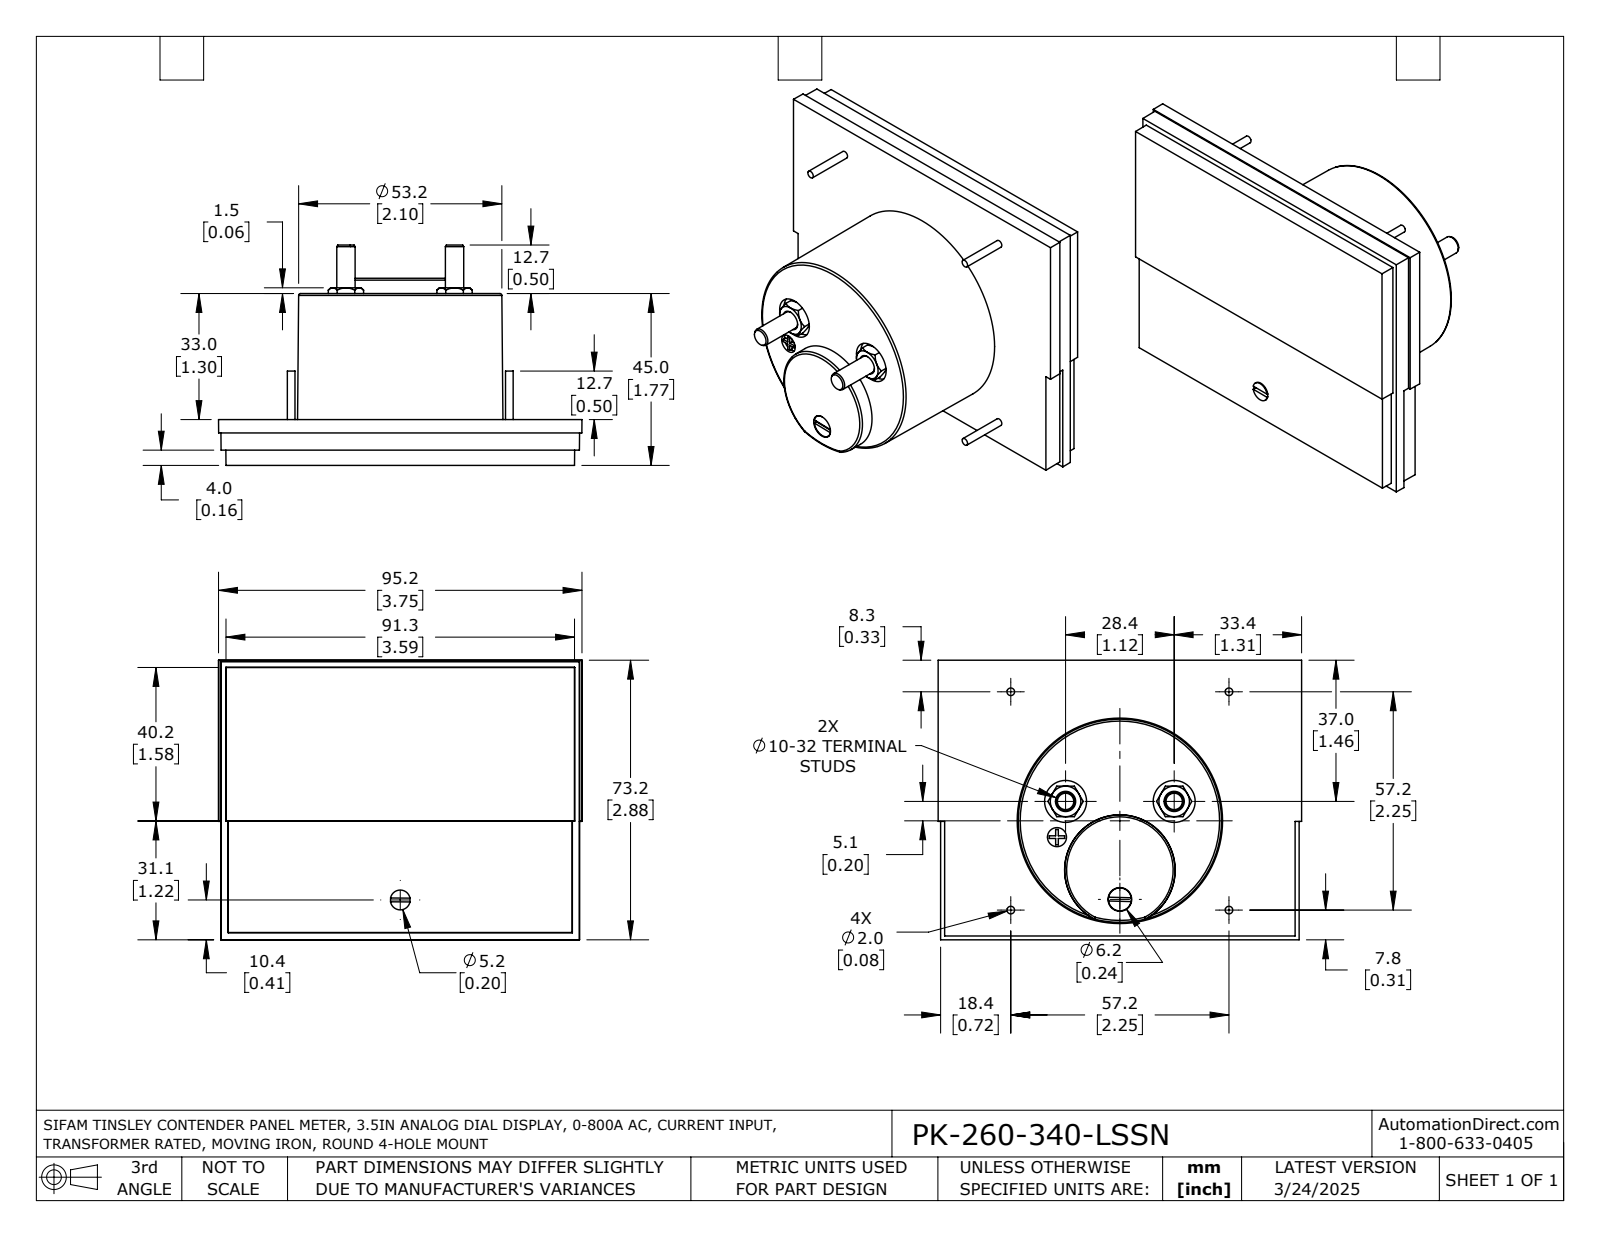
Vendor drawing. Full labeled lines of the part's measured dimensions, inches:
Part name (STEP PRODUCT): PK-260-340-LSSN
STEP written by: SolidWorks 2021 (AUTOMOTIVE_DESIGN)
Units: inches
Bodies: 1 solid, 163 faces (76 planar, 31 cylindrical, 56 other)
Overall size (bounding box): 3.748 × 2.882 × 2.272
Volume: 9.446 in³ · Surface area: 38.39 in²
Round holes (diameter × count): ⌀0.433 ×2, ⌀0.197 ×1, ⌀0.244 ×1
Round bosses / shafts (diameter × count): ⌀0.079 ×4, ⌀0.189 ×2, ⌀0.236 ×1, ⌀0.205 ×1
Partial cylindrical surfaces — rounded edges, fillets, slot ends (radius × count): R0.1 ×1
Main face-to-face distances: 0.472, 0.03, 0.443, 1.772, 1.299, 1.742, 0.157, 0.073, 0.315, 1.457
Hole centre spacings: 1.155, 0.379, 0.912, 1.12, 1.263
